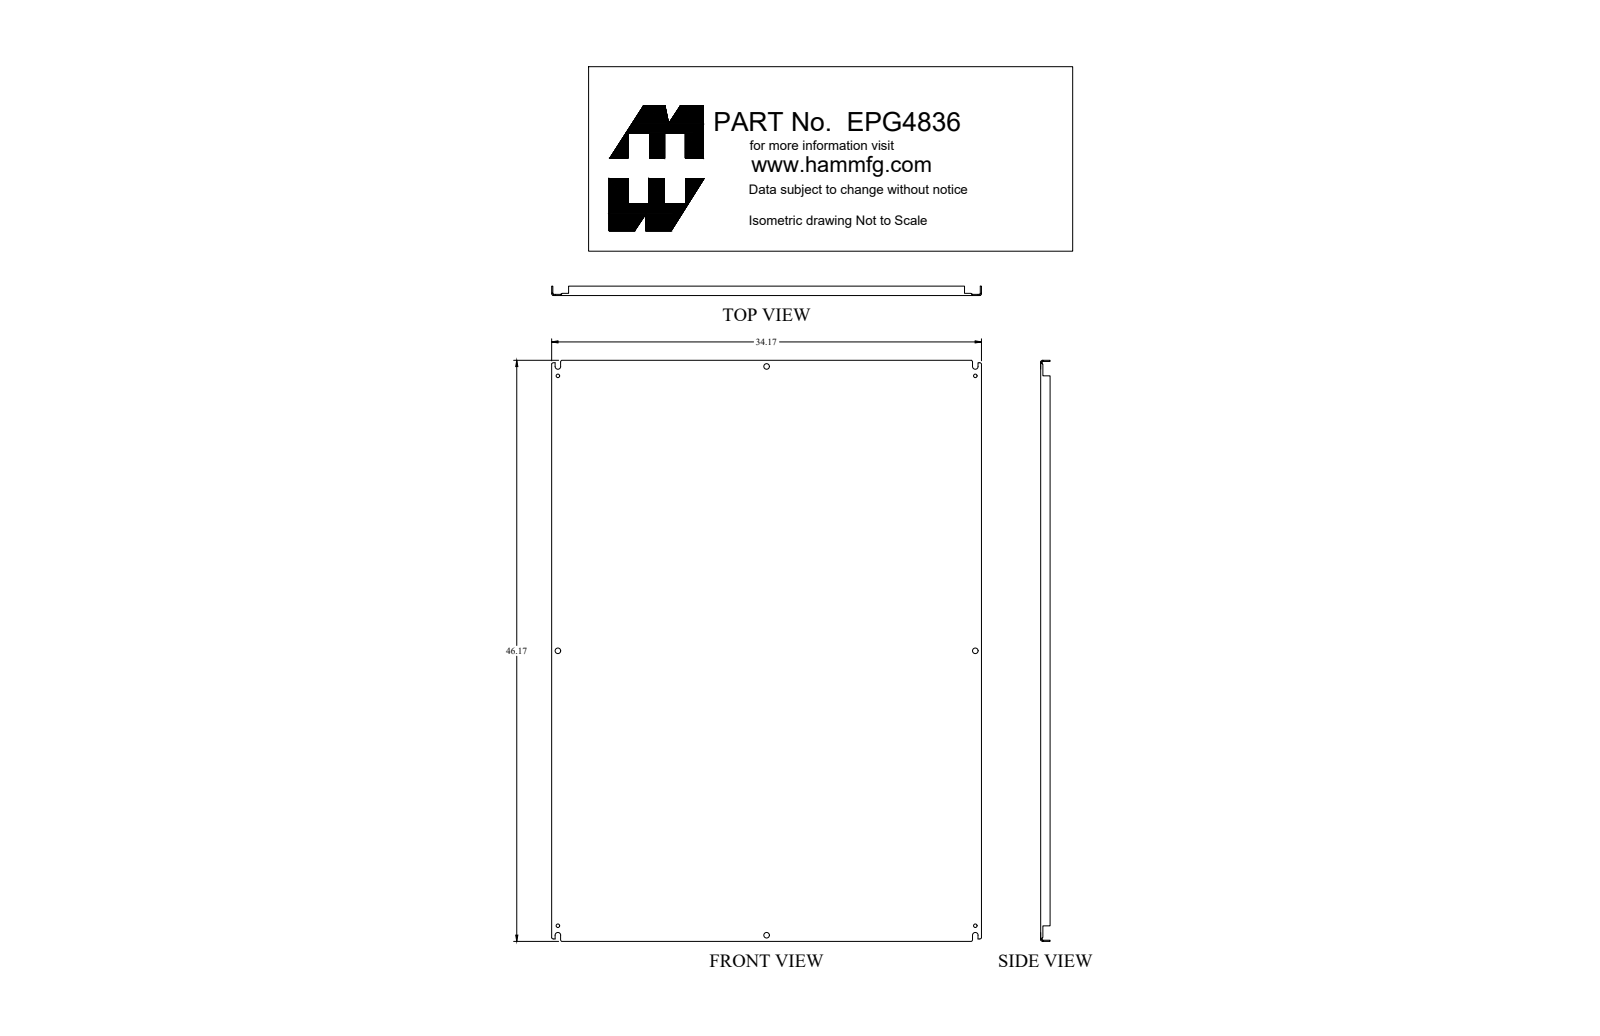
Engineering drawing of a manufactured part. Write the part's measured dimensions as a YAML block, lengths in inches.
part_name: "EPG4836"
step_written_by: "SolidWorks 2018 (AUTOMOTIVE_DESIGN)"
units: inches
bodies: {solids: 1, faces: 136, planar: 74, cylindrical: 46, other: 16}
overall_size: [46.17, 34.17, 0.75]
volume: 158.4
surface_area: 3352
round_holes:
  - {diameter: 0.281, count: 4}
  - {diameter: 0.437, count: 4}
partial_cylinders:
  - {radius: 0.048, count: 4}
  - {radius: 0.063, count: 4}
  - {radius: 0.143, count: 4}
  - {radius: 0.219, count: 4}
face_to_face_distances: [0.095, 34.075, 46.075, 34.17, 33.98, 45.98, 46.17, 0.75, 0.655, 0.171]
hole_center_spacings: [16.611, 21.844, 28.033, 39.732, 47.435, 33.188, 43.688, 54.865]
